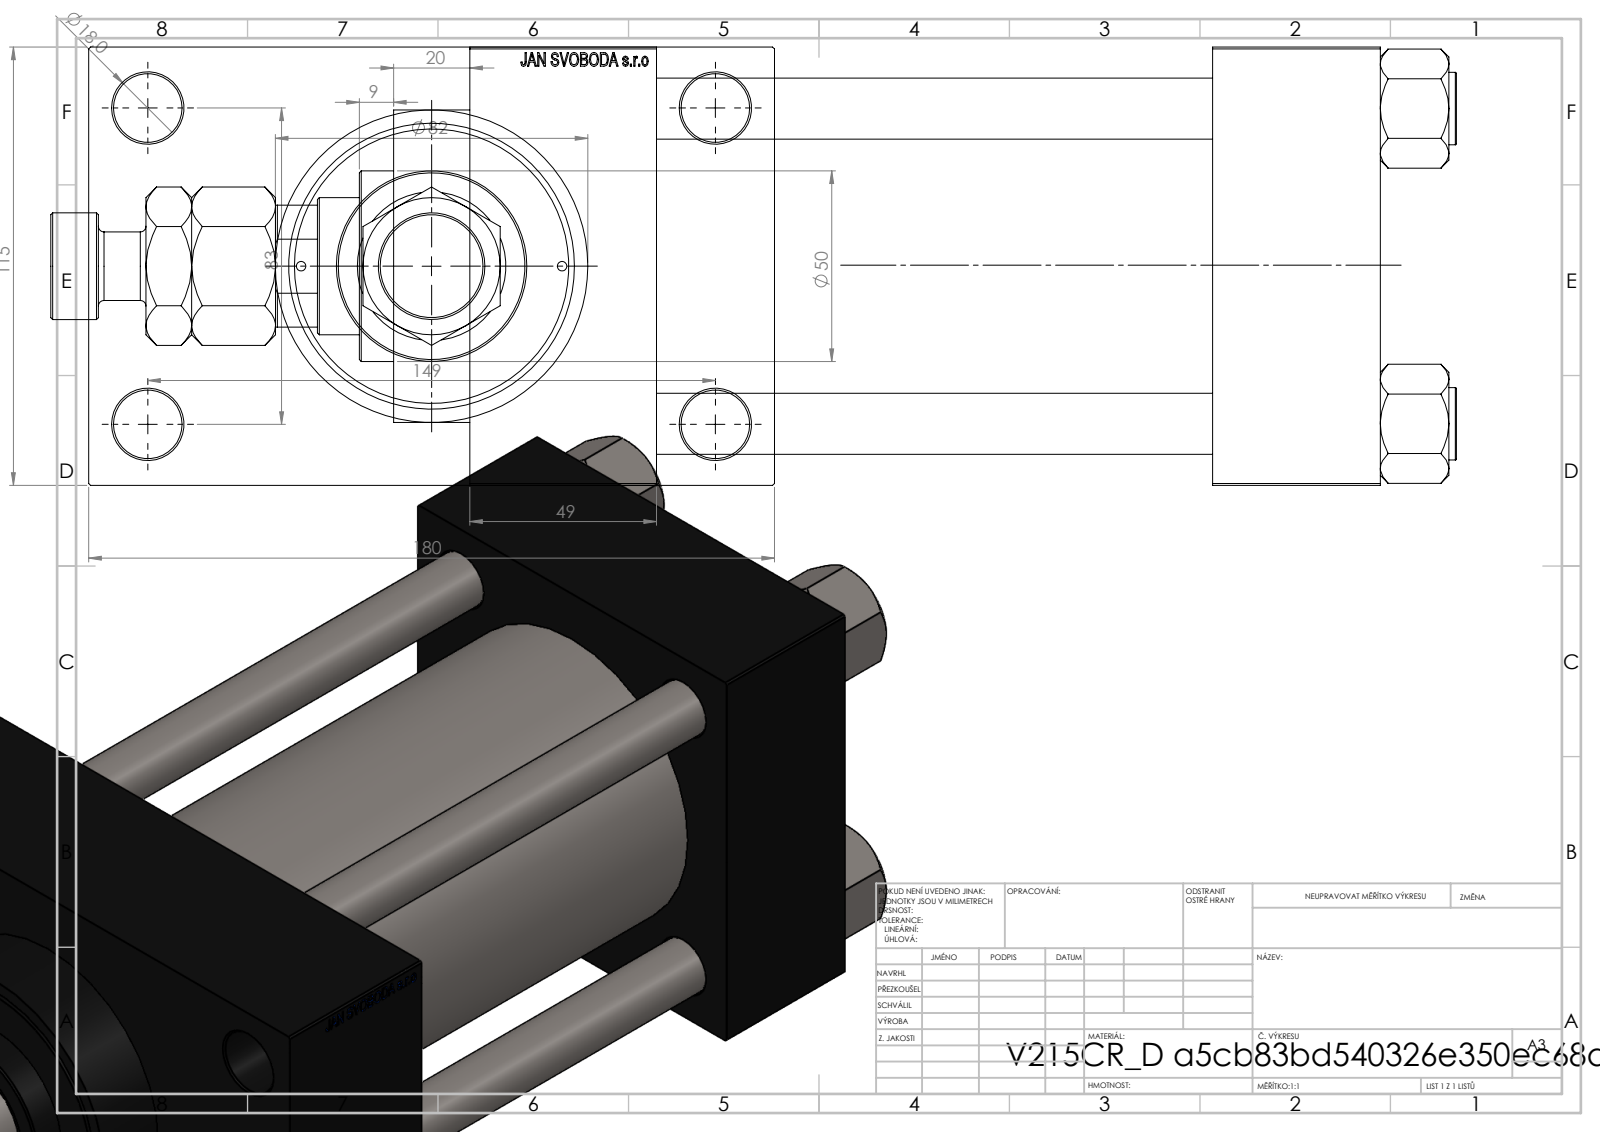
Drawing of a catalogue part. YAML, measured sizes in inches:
part_name: "MFA; V215CR_D_TYCINKA; V215CR_D_Body; V215CR_VCP_D (+2 more)"
step_written_by: "SolidWorks 2019 (CONFIG_CONTROL_DESIGN)"
units: inches
bodies: {solids: 12, faces: 1211, planar: 563, cylindrical: 96, other: 552}
overall_size: [14.528, 7.087, 4.528]
volume: 136.4
surface_area: 576.8
round_holes:
  - {diameter: 0.63, count: 4}
  - {diameter: 0.709, count: 4}
  - {diameter: 0.098, count: 2}
  - {diameter: 0.276, count: 2}
  - {diameter: 1.041, count: 2}
  - {diameter: 1.378, count: 2}
  - {diameter: 1.004, count: 1}
  - {diameter: 1.417, count: 1}
  - {diameter: 1.535, count: 1}
  - {diameter: 2.402, count: 1}
  - {diameter: 2.835, count: 1}
  - {diameter: 3.15, count: 1}
round_bosses_or_shafts:
  - {diameter: 0.748, count: 4}
  - {diameter: 3.386, count: 1}
  - {diameter: 3.228, count: 1}
  - {diameter: 1.969, count: 1}
  - {diameter: 1.102, count: 1}
  - {diameter: 0.709, count: 1}
partial_cylinders:
  - {radius: 0.689, count: 1}
face_to_face_distances: [4.528, 5.748, 7.677, 1.929, 1.732, 7.48, 9.409, 1.28, 5.807, 3.937]
hole_center_spacings: [1.305, 1.652, 2.276, 2.302, 3.256, 3.357, 3.393, 3.513]
